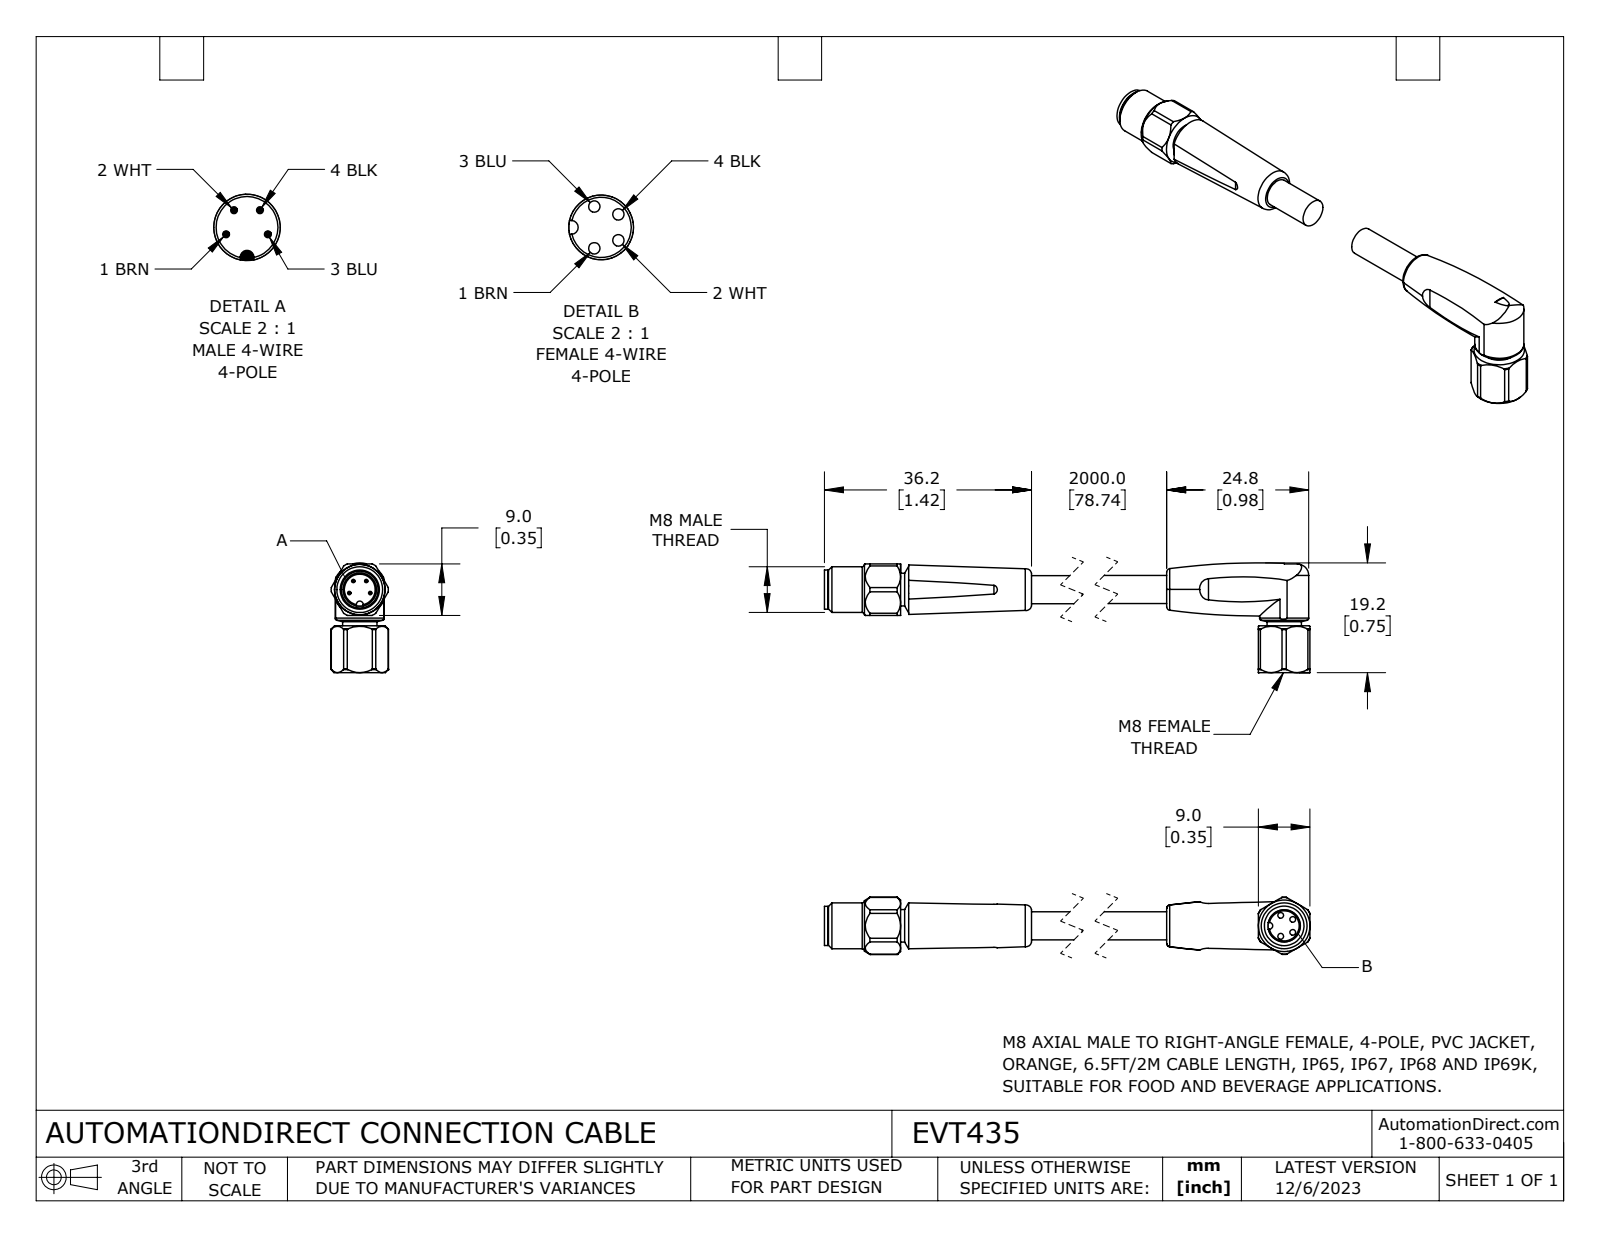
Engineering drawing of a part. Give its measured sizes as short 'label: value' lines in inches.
name: EVT435; EVT435_FEMALE; EVT435_MALE
written by: SolidWorks 2023 (CONFIG_CONTROL_DESIGN)
unit: in
bodies: 2 solids, 172 faces (52 planar, 59 cylindrical, 61 other)
size: 3.76 × 0.755 × 0.394
volume: 0.254 in³; area: 4.6 in²
holes: 4× ⌀0.039, 1× ⌀0.228, 1× ⌀0.272
bosses: 4× ⌀0.023, 2× ⌀0.193, 1× ⌀0.339, 1× ⌀0.315, 1× ⌀0.27, 1× ⌀0.248, 1× ⌀0.236, 1× ⌀0.224
rounds: 2× R0.024, 2× R0.126, 2× R0.133, 1× R0.196, 1× R0.197
face distances: 0.354, 0.354, 3.236, 2.882, 0.323, 0.748, 0.425, 0.394, 0.071, 0.327
hole spacings: 0.074, 0.076, 0.087, 0.143, 0.089, 0.143
